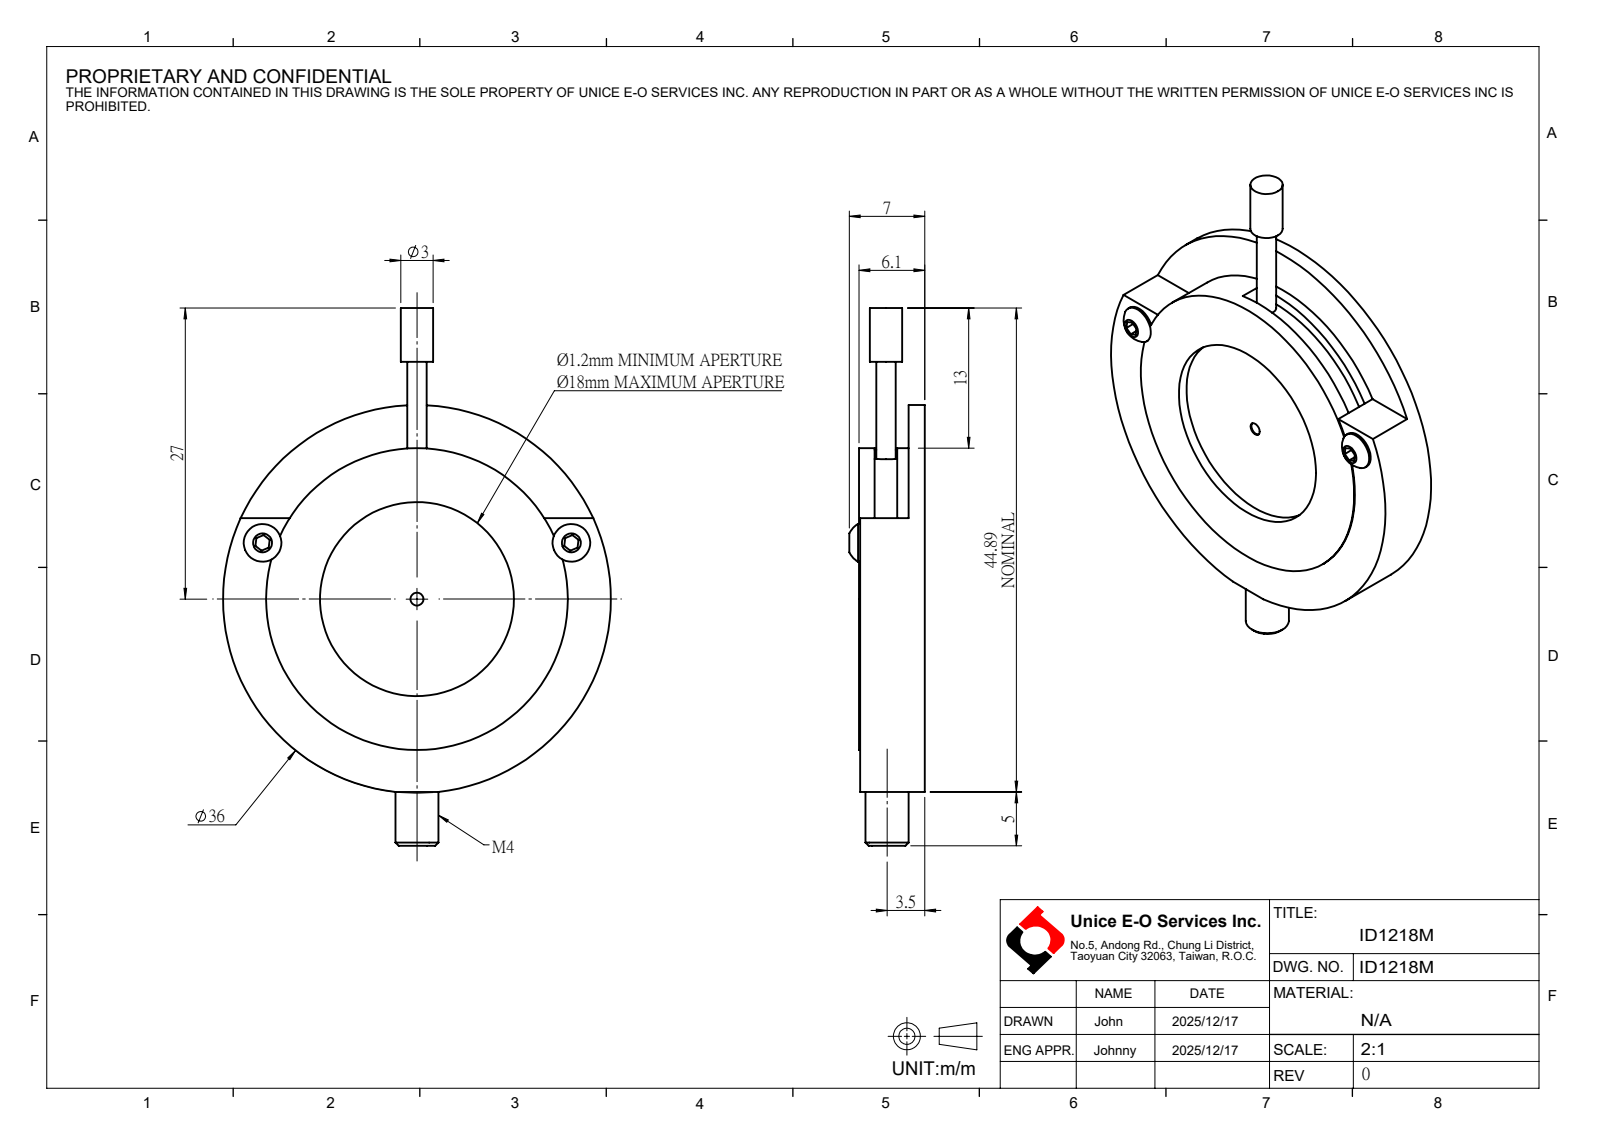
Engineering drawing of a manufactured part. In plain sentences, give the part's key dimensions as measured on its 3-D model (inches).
The part is named "ID1218M". Its 3-D file was written by "SolidWorks 2024 (CONFIG_CONTROL_DESIGN)". It is 5 solids with 99 faces: 48 planar, 39 cylindrical and 12 other. Overall it measures 1.964 by 1.417 by 0.276 inches. Its volume is 0.218 cubic inches and its surface area 6.867 square inches. Round holes: 2 of diameter 0.063, 1 of diameter 0.047, 1 of diameter 0.13, 1 of diameter 0.709, 1 of diameter 0.984, 1 of diameter 1.024, 1 of diameter 1.102. Round bosses or shafts: 2 of diameter 0.138, 2 of diameter 0.079, 1 of diameter 1.417, 1 of diameter 0.157, 1 of diameter 0.118, 1 of diameter 0.071. The main face-to-face distances are 0.039, 0.157, 0.154, 0.197, 0.043, 0.24, 0.083, 0.118, 0.236, 0.035. The hole center spacings are 0.6, 1.128.
